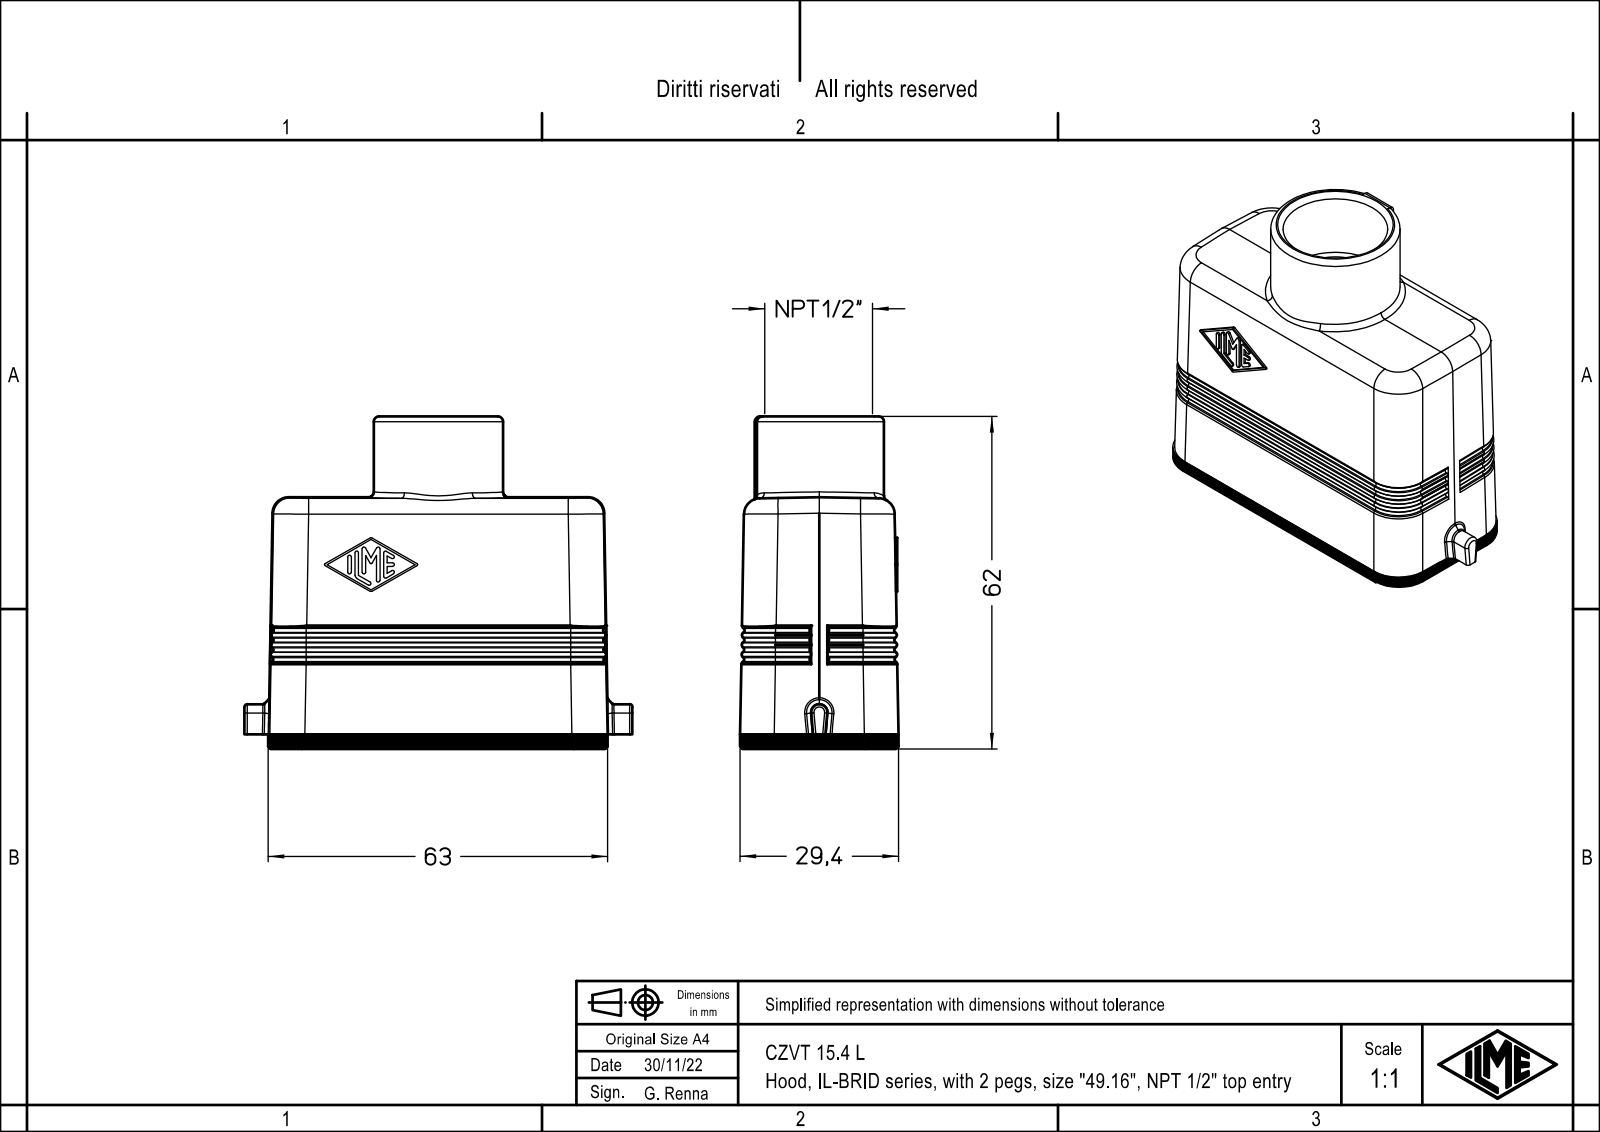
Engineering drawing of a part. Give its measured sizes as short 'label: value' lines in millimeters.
name: CZVT 15.4 L
written by: Creo Elements/Direct Modeling 20.1B 02-Apr-2019 (C) Parametric Technology GmbH (AUTOMOTIVE_DESIGN)
unit: mm
bodies: 1 solid, 482 faces (171 planar, 155 cylindrical, 156 other)
size: 72 × 61.7 × 29.4
volume: 27 083 mm³; area: 20 910 mm²
holes: 1× ⌀16, 1× ⌀20.95
bosses: 1× ⌀24
rounds: 66× R0.5, 15× R0.33, 12× R2, 9× R1.5, 8× R4.3, 4× R3.4, 4× R3.5, 4× R6.2
face distances: 7.05, 7.25, 44.2, 2.9, 2.7, 0.9, 26.5, 24.7, 14.2, 30
